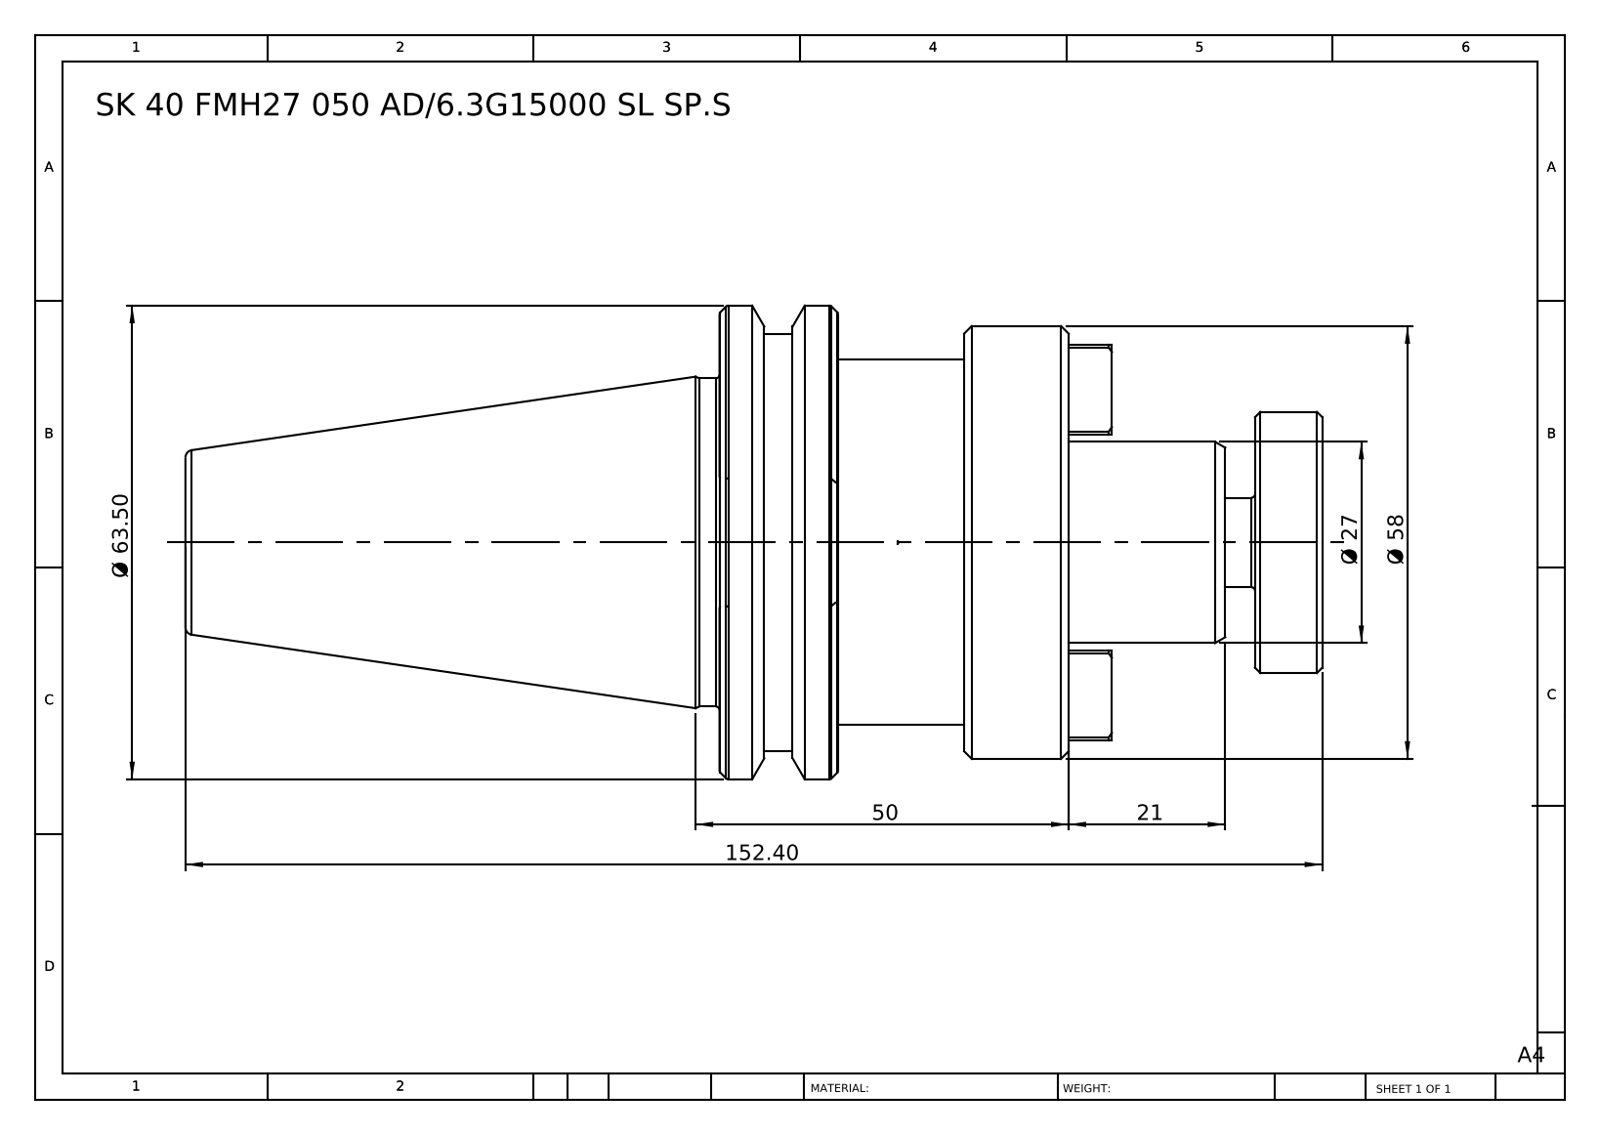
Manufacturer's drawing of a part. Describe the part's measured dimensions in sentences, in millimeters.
The part is named "SK40 FMH27 050 AD-6.3G15000 SL SP.S". Its 3-D file was written by "SolidWorks 2014 (CONFIG_CONTROL_DESIGN)". It is 1 solid with 119 faces: 37 planar, 20 cylindrical and 62 other. Overall it measures 152.4 by 63.5 by 63.5 millimeters. Its volume is 208 487 cubic millimeters and its surface area 28 389 square millimeters. Round bosses or shafts: 1 of diameter 63.5, 1 of diameter 58, 1 of diameter 56, 1 of diameter 49, 1 of diameter 44, 1 of diameter 35, 1 of diameter 27, 1 of diameter 12. Partial cylindrical surfaces (rounded edges, fillets, slot ends): 1 of radius 8.05. The main face-to-face distances are 46.8, 30.9, 15.9, 34, 64.9, 80.8, 9, 25, 55.9, 71.8.
